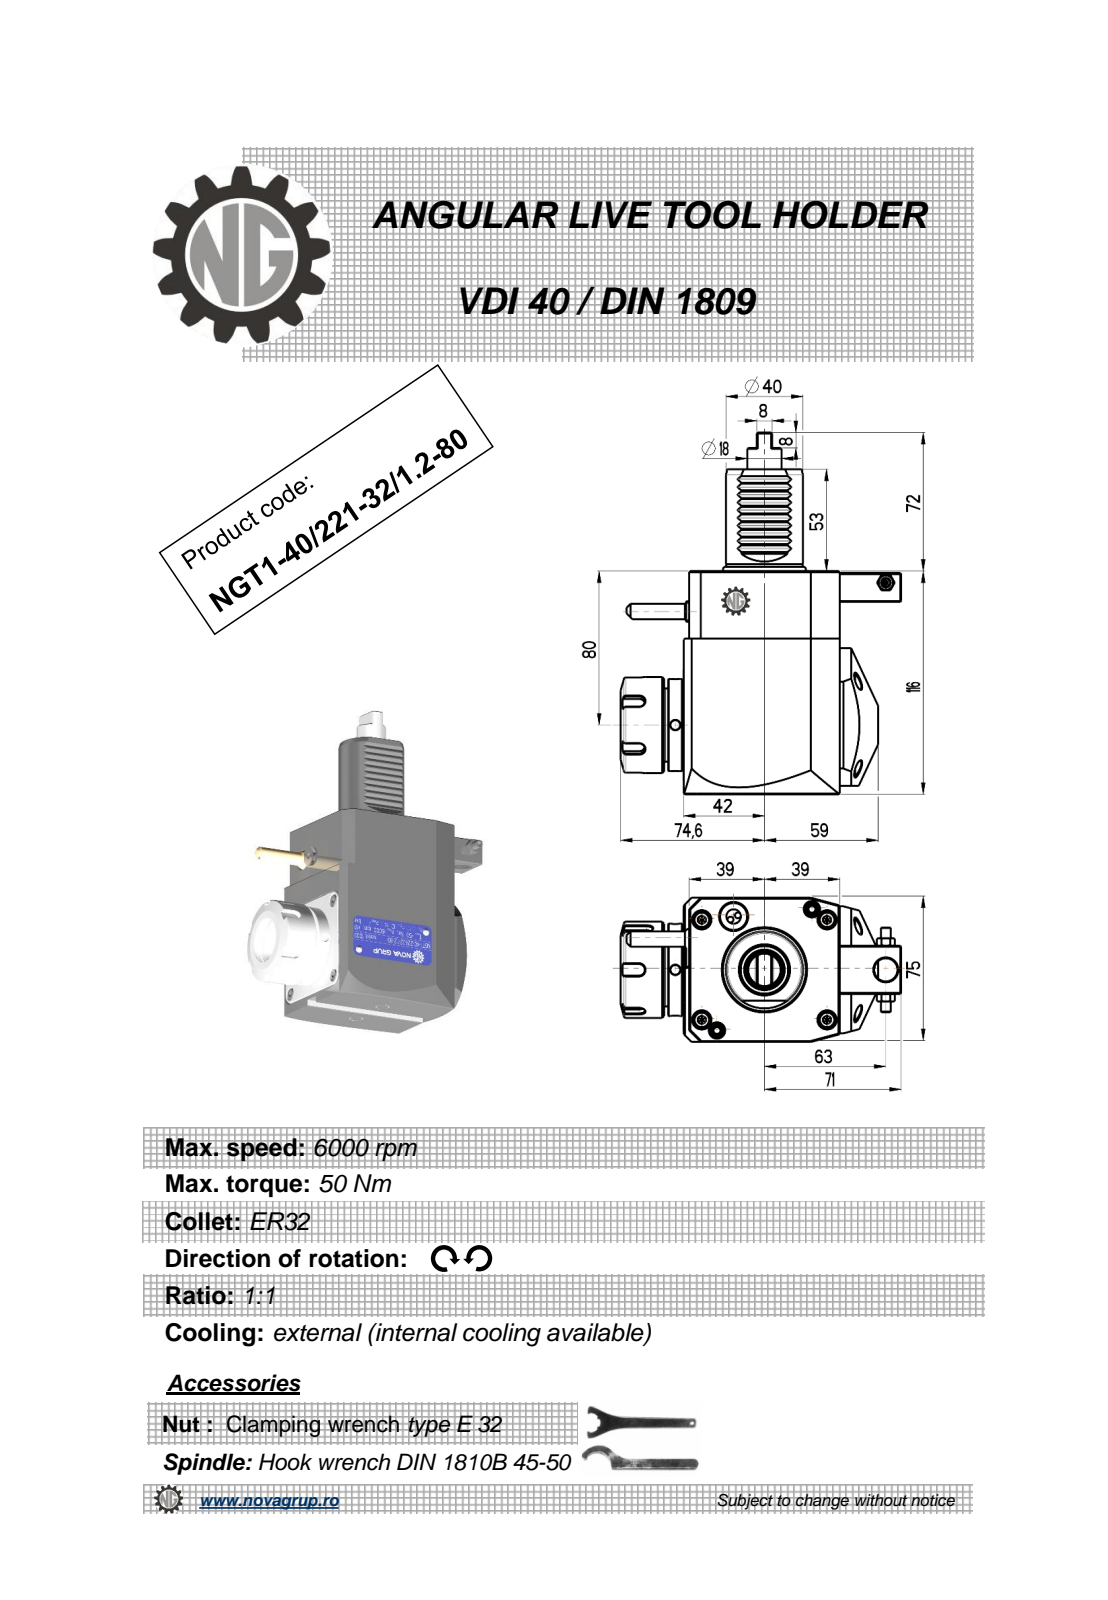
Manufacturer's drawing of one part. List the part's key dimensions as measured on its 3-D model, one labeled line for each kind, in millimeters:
Part name (STEP PRODUCT): NGT1_40_221_32_1_2_80
STEP written by: PRO/ENGINEER BY PARAMETRIC TECHNOLOGY CORPORATION, 2010280 (CONFIG_CONTROL_DESIGN)
Units: millimetres
Bodies: 1 solid, 409 faces (193 planar, 89 cylindrical, 127 other)
Overall size (bounding box): 188 × 145.6 × 76.6
Volume: 870 955 mm³ · Surface area: 69 800 mm²
Round holes (diameter × count): ⌀5 ×3, ⌀3 ×1, ⌀4.2 ×1, ⌀9.5 ×1, ⌀12 ×1, ⌀27 ×1
Round bosses / shafts (diameter × count): ⌀50 ×1, ⌀48 ×1, ⌀41 ×1, ⌀40 ×1, ⌀17.8 ×1, ⌀11.2 ×1, ⌀8.96 ×1, ⌀8 ×1
Partial cylindrical surfaces — rounded edges, fillets, slot ends (radius × count): R0.26 ×12, R0.3 ×10, R0.22 ×6, R3 ×5, R0.8 ×2, R0.5 ×1, R40 ×1
Main face-to-face distances: 75, 116, 81, 3, 78, 2.8, 80.8, 25, 4.5, 7.5
Hole centre spacings: 20.93, 61.13, 72.5, 109.25, 131.95
